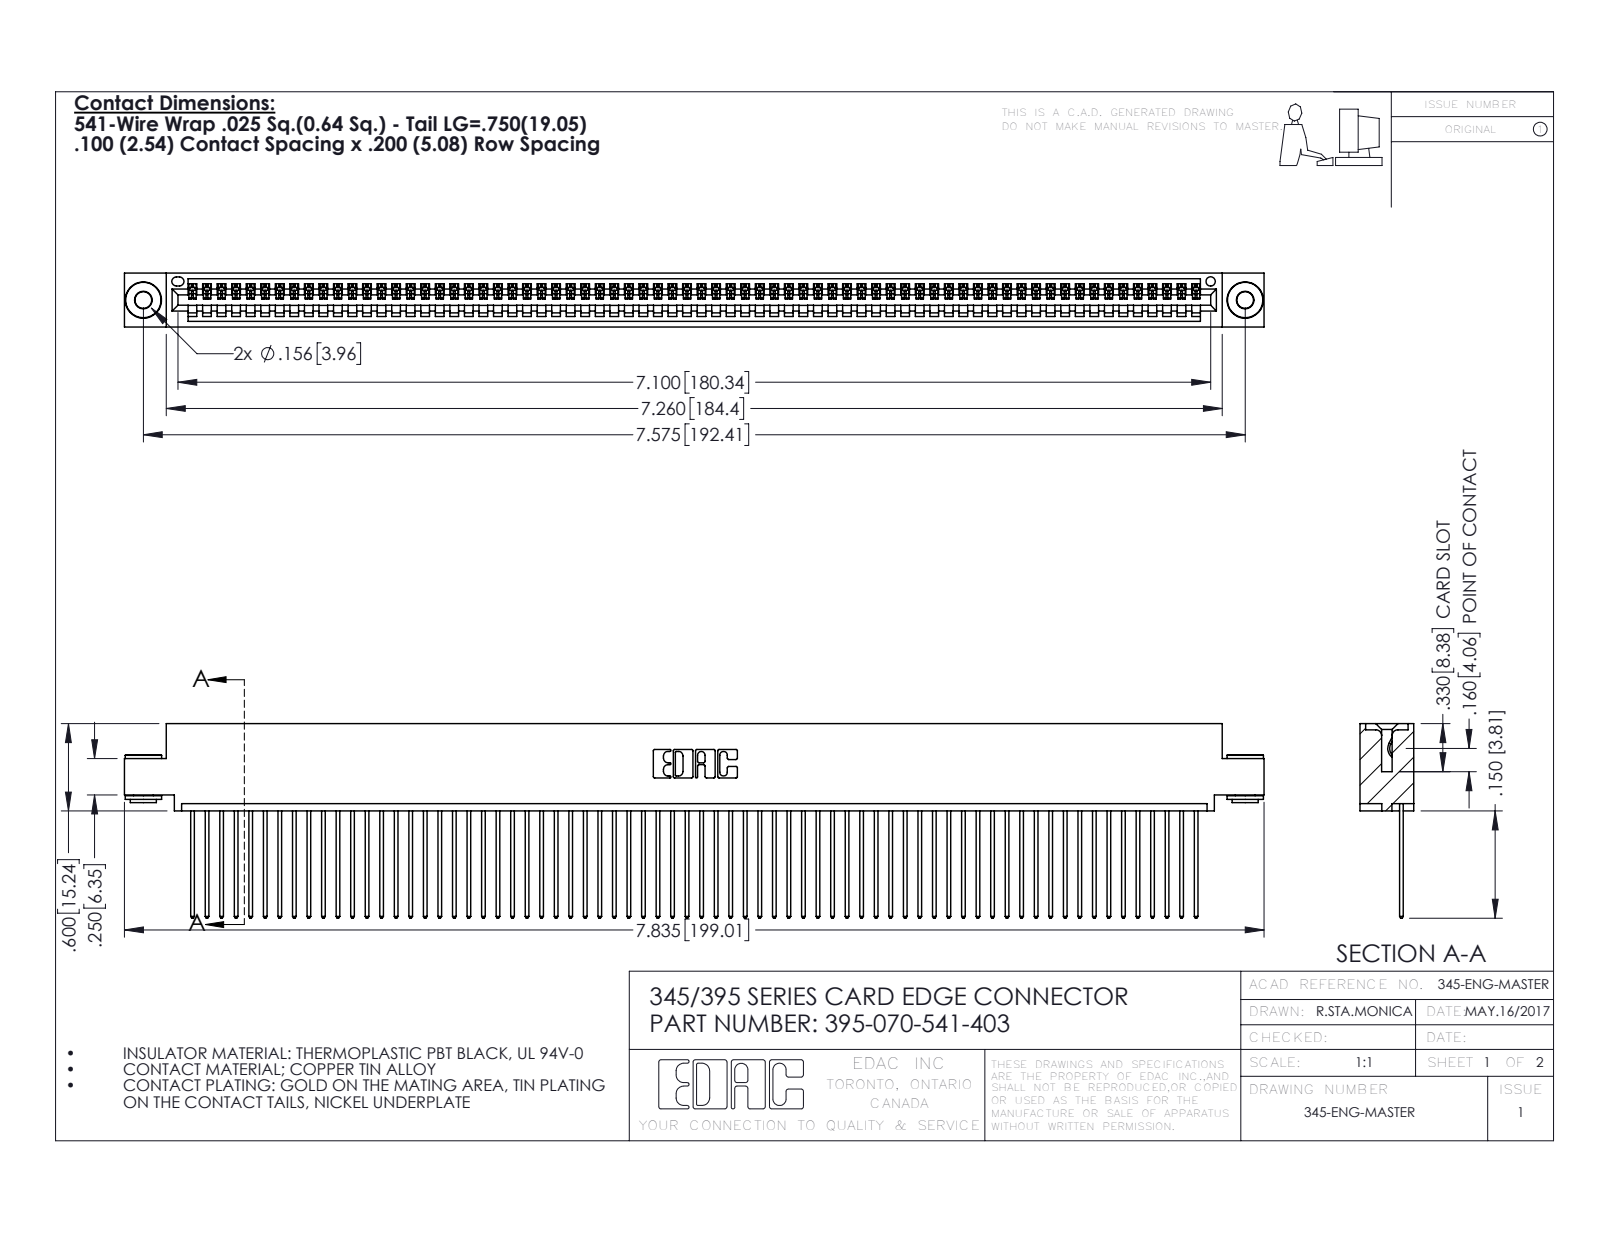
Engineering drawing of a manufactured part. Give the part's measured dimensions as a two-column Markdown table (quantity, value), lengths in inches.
| quantity | value |
| --- | --- |
| part name | 345-292-001_345-293-141; 395-070-541-403; 345-250-002_345-250-002-102; 345 Part_0.110 Offset - 0.156 Dia-TH |
| STEP written by | SolidWorks 2016 (CONFIG_CONTROL_DESIGN) |
| units | inches |
| bodies | 73 solids, 4228 faces (2894 planar, 1326 cylindrical, 8 other) |
| overall size | 7.835 × 1.337 × 0.37 |
| volume | 1.178 in³ |
| surface area | 42.93 in² |
| round holes (diameter × count) | 0.116 × 2, 0.156 × 2, 0.064 × 1 |
| round bosses / shafts (diameter × count) | 0.25 × 2, 0.18 × 2, 0.136 × 2 |
| partial cylindrical surfaces (radius × count) | 0.006 × 140, 0.01 × 140, 0.01 × 22, 0.007 × 6, 0.031 × 6, 0.026 × 3, 0.031 × 2, 0.04 × 2 |
| main face-to-face distances | 0.072, 0.298, 0.025, 0.098, 0.272, 0.37, 0.2, 0.225, 0.149, 0.072 |
| hole center spacings | 0.27, 7.339, 7.575 |
